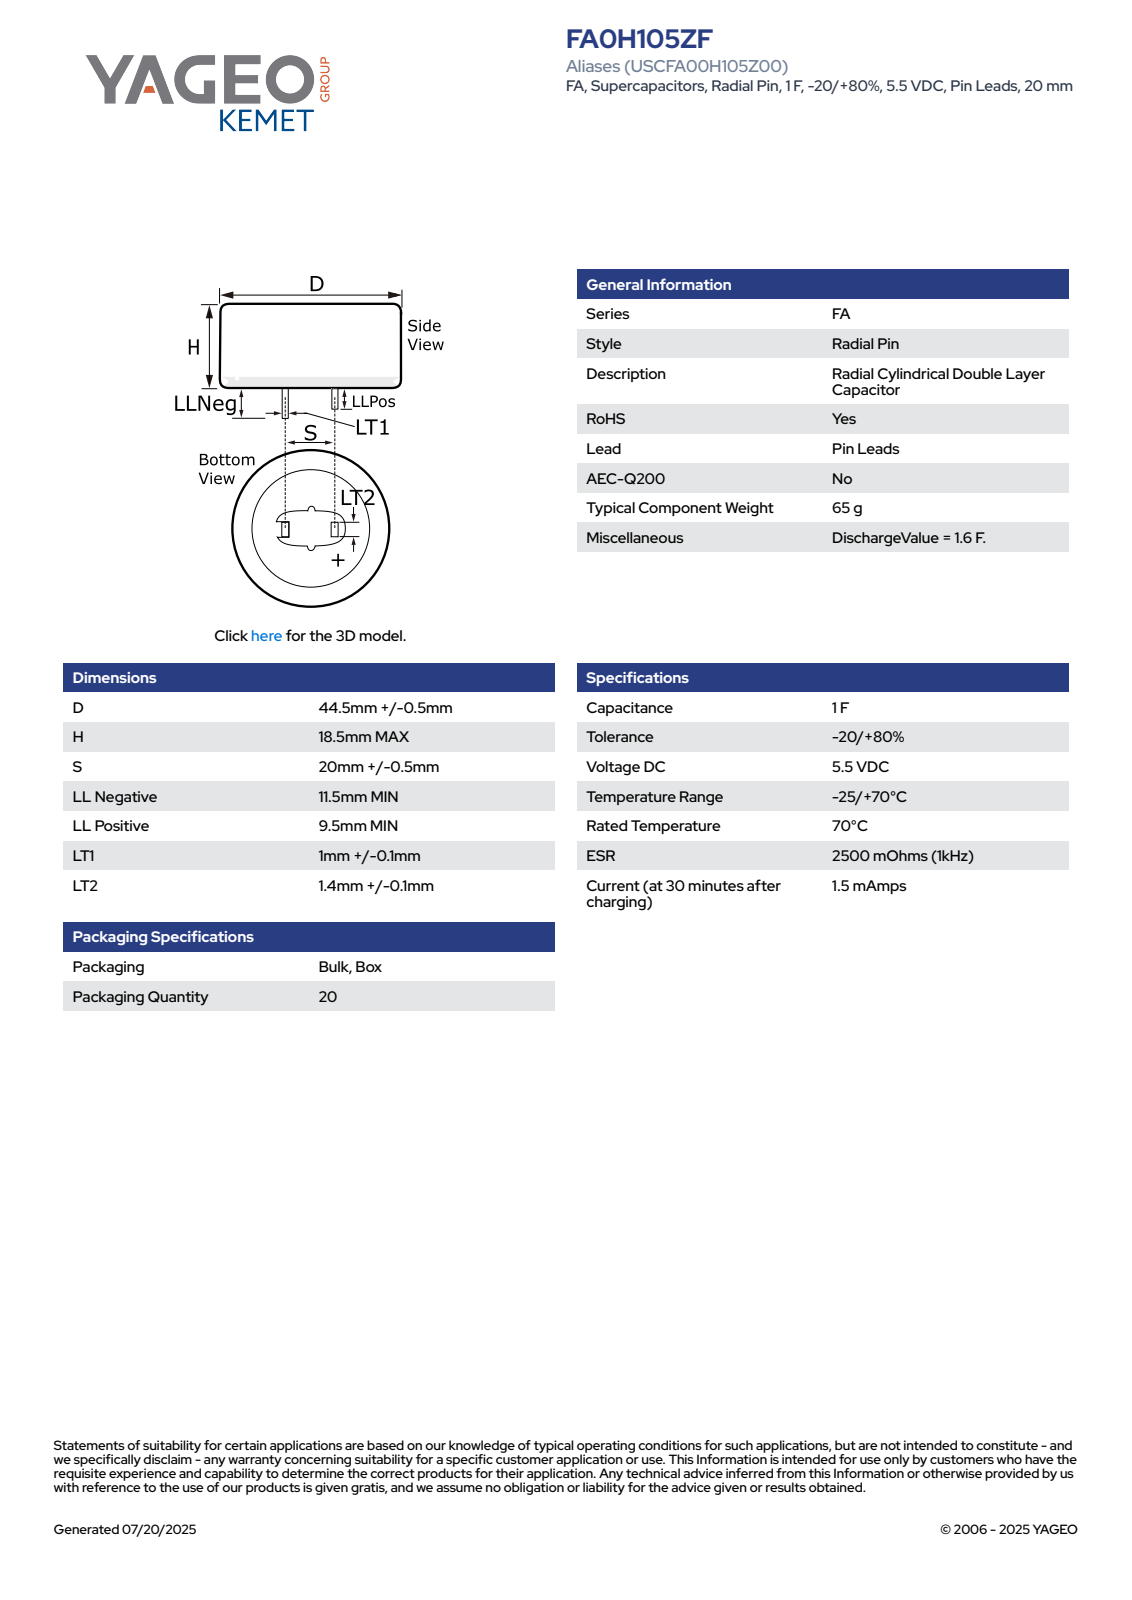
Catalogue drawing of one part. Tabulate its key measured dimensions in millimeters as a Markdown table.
| quantity | value |
| --- | --- |
| part name | CDR_LPLLN_D45L18.5S20LLNEG11.5LLPOS9.5LT11.1LT21.5 |
| STEP written by | SolidWorks 2014 (AUTOMOTIVE_DESIGN) |
| units | millimeters |
| bodies | 1 solid, 78 faces (70 planar, 4 cylindrical, 4 other) |
| overall size | 45 × 45 × 30 |
| volume | 29 373 mm³ |
| surface area | 5 760 mm² |
| round bosses / shafts (diameter × count) | 45 × 1 |
| partial cylindrical surfaces (radius × count) | 22.51 × 1 |
| main face-to-face distances | 18.5, 1.1, 20, 1.5, 21.1, 18.9, 18.49, 2, 11.5, 29.99 |
